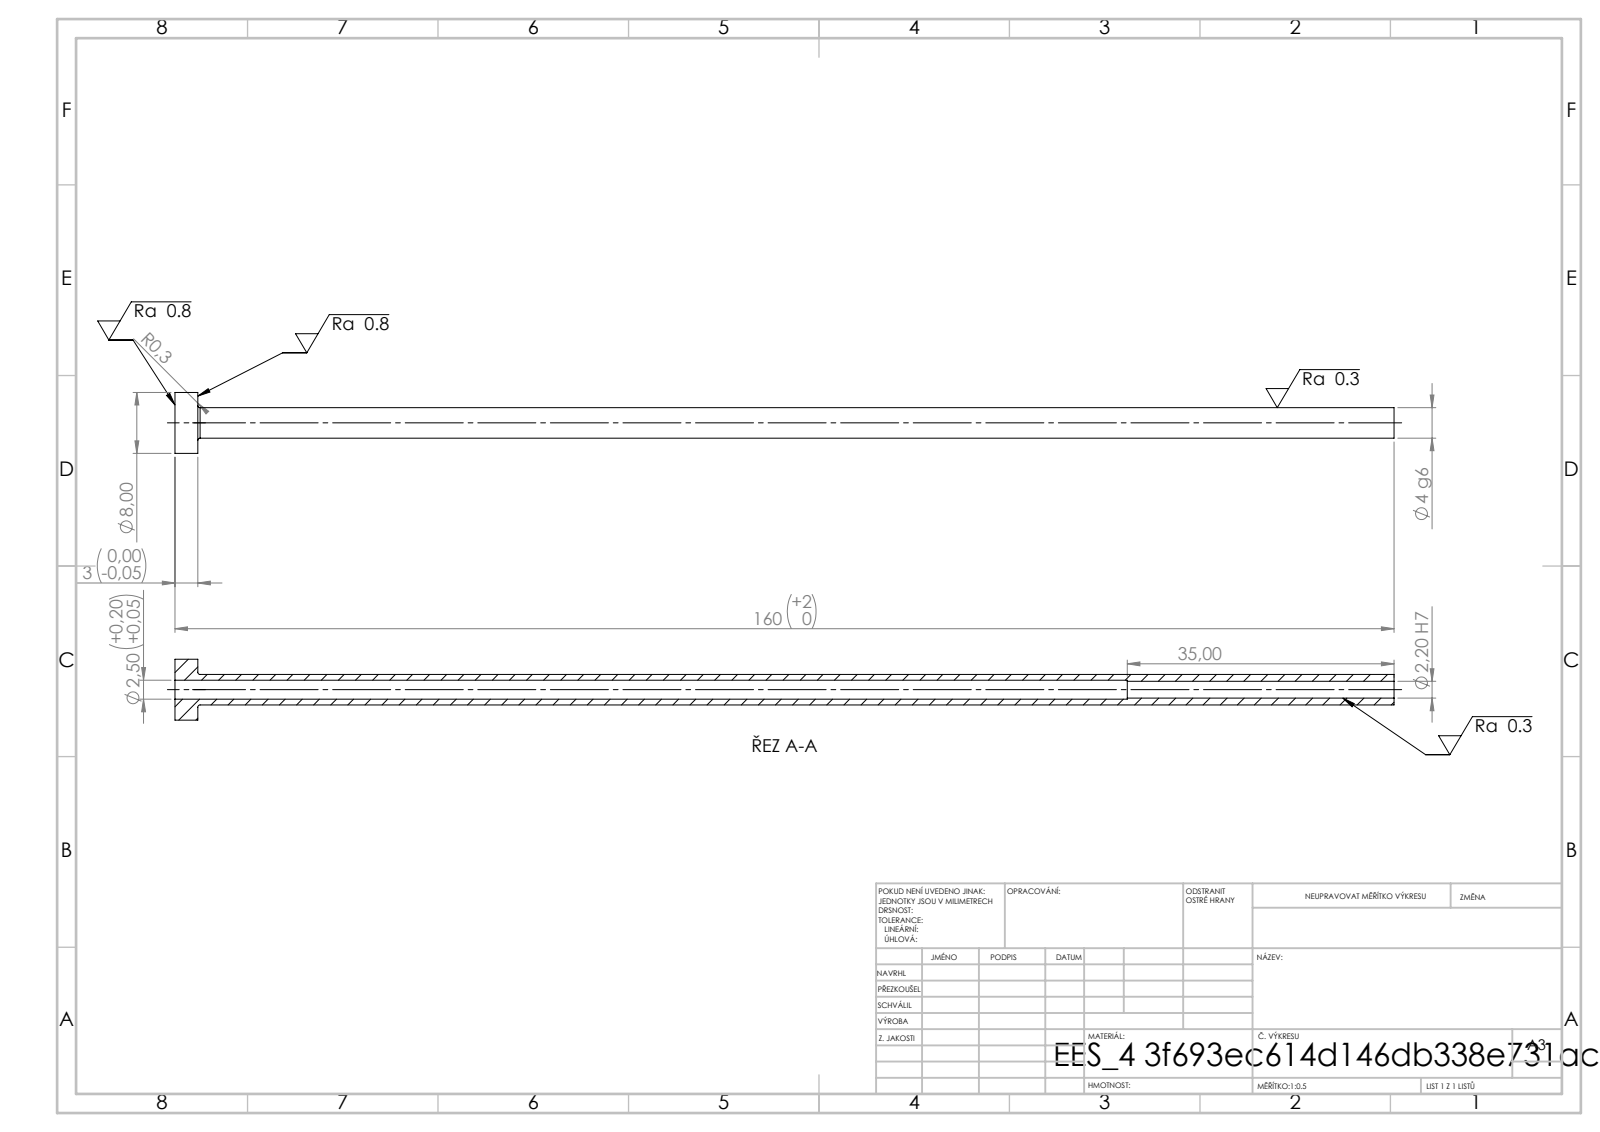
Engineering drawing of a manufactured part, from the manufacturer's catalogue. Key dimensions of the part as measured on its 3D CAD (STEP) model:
STEP written by: SolidWorks 2019 (CONFIG_CONTROL_DESIGN)
Units: millimetres
Bodies: 1 solid, 14 faces (4 planar, 8 cylindrical, 2 other)
Overall size (bounding box): 160 × 8 × 8
Volume: 1 377 mm³ · Surface area: 3 363 mm²
Round holes (diameter × count): ⌀2.2 ×1, ⌀2.5 ×1
Round bosses / shafts (diameter × count): ⌀8 ×1, ⌀4 ×1
Main face-to-face distances: 3, 160, 157, 125, 122, 35
